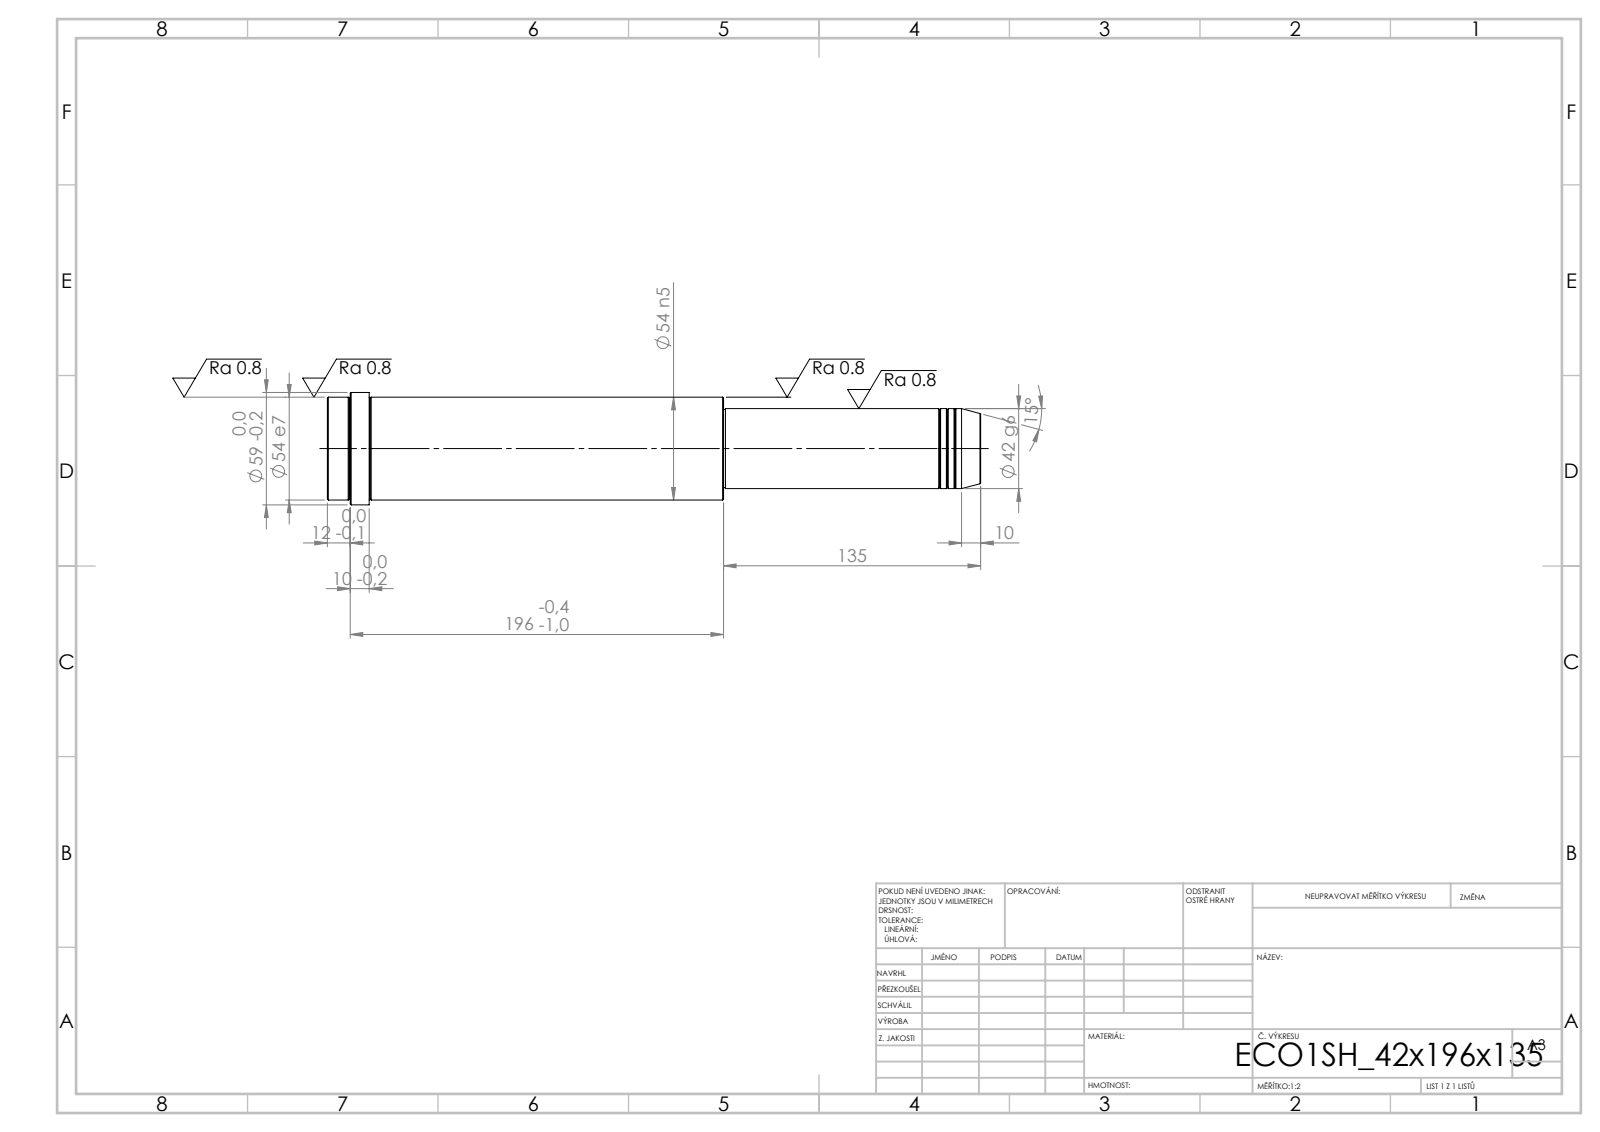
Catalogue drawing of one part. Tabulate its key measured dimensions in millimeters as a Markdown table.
| quantity | value |
| --- | --- |
| STEP written by | SolidWorks 2019 (CONFIG_CONTROL_DESIGN) |
| units | millimeters |
| bodies | 1 solid, 52 faces (6 planar, 16 cylindrical, 30 other) |
| overall size | 343 × 59 × 59 |
| volume | 665 726 mm³ |
| surface area | 58 716 mm² |
| round bosses / shafts (diameter × count) | 59 × 1, 54 × 1, 42 × 1, 41 × 1 |
| main face-to-face distances | 343, 135, 208, 321, 186, 22, 331, 196, 10, 12 |
